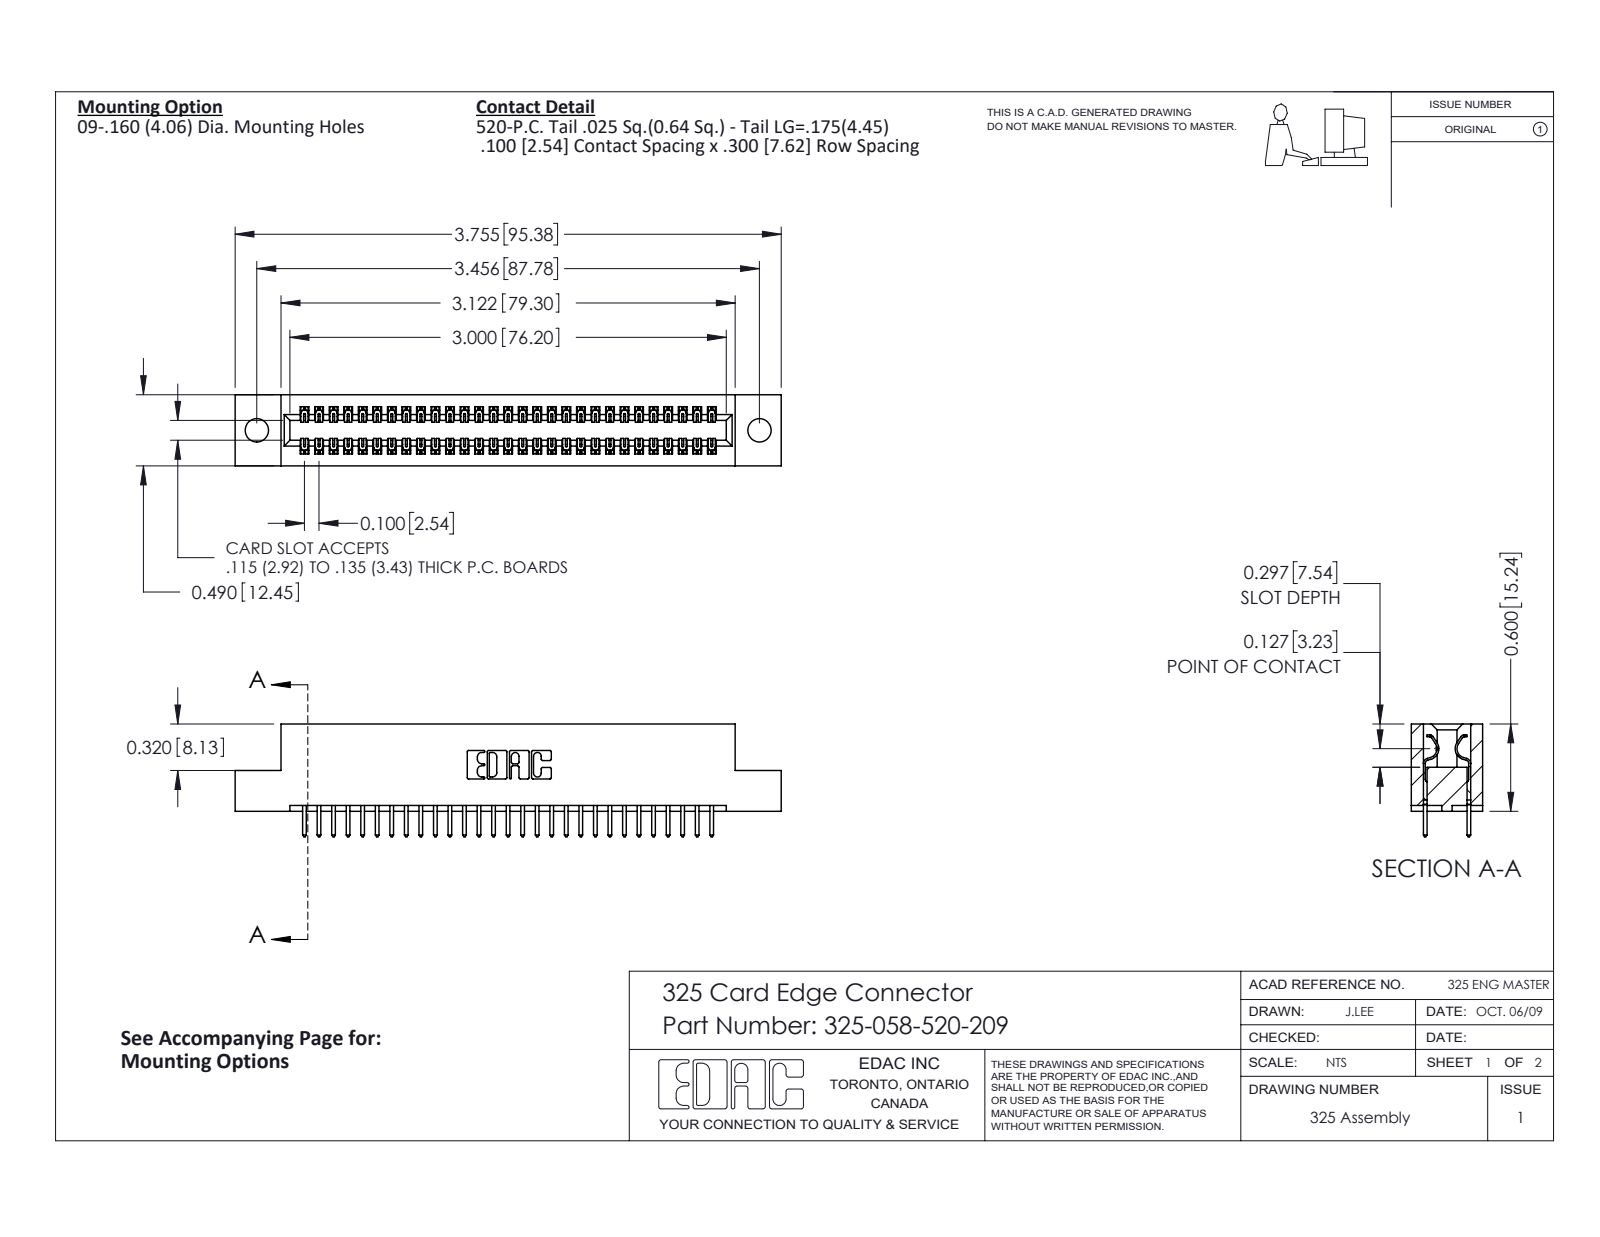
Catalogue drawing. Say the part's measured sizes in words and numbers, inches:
The part is named "325 Part_.160 TH; 325-058-520-209; 325-292-001_325-293-120". Its 3-D file was written by "SolidWorks 2016 (CONFIG_CONTROL_DESIGN)". It is 59 solids with 3130 faces: 2158 planar, 972 cylindrical and 0 other. Overall it measures 3.755 by 0.775 by 0.49 inches. Its volume is 0.73 cubic inches and its surface area 21.65 square inches. Round holes: 2 of diameter 0.16. Partial cylindrical surfaces (rounded edges, fillets, slot ends): 87 of radius 0.006, 58 of radius 0.01, 22 of radius 0.01, 6 of radius 0.007, 6 of radius 0.031, 3 of radius 0.026, 2 of radius 0.014, 2 of radius 0.022. The main face-to-face distances are 0.083, 0.407, 0.3, 0.49, 0.107, 0.383, 0.025, 0.325, 0.04, 0.275. The hole center spacings are 3.456.
